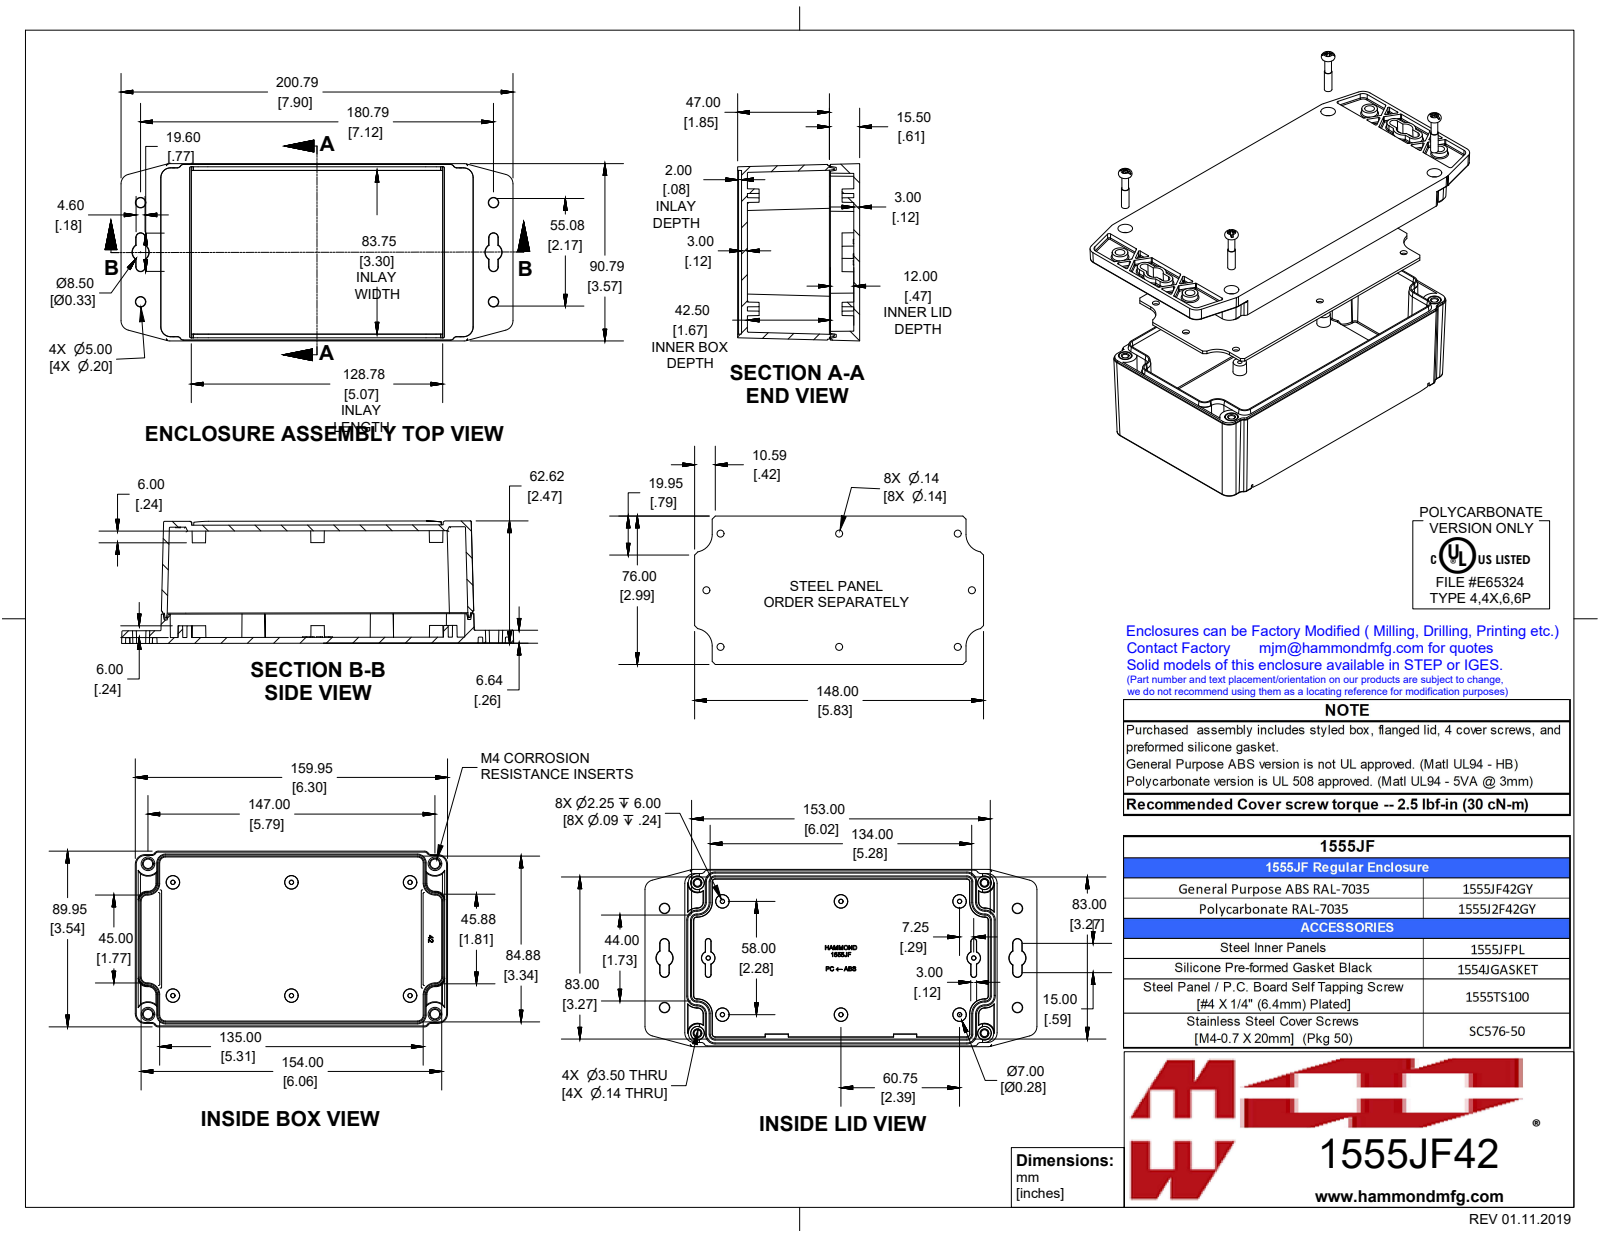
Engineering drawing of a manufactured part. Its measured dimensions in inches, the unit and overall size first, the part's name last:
Units: inches
Overall size (bounding box): 7.905 × 3.574 × 2.461
Round holes (diameter × count): ⌀0.128 ×4, ⌀0.138 ×4, ⌀0.276 ×4, ⌀0.374 ×1
Round bosses / shafts (diameter × count): ⌀0.25 ×4, ⌀0.218 ×4, ⌀0.21 ×4, ⌀0.153 ×4, ⌀0.135 ×4
Partial cylindrical surfaces — rounded edges, fillets, slot ends (radius × count): R0.02 ×104, R0.197 ×16, R0.089 ×4, R0.187 ×3, R1.988 ×1, R2.016 ×1, R2.126 ×1, R2.13 ×1
Main face-to-face distances: 0.118, 2.264, 2.382, 2.146, 0.059, 0.079, 0.472, 1.791, 1.673, 0.591
Hole centre spacings: 3.031, 5.787, 6.533
Volume: 13.23 in³ · Surface area: 226.9 in²
Bodies: 10 solids, 1338 faces (633 planar, 227 cylindrical, 478 other)
Part name (STEP PRODUCT): 1555JF42GY
STEP written by: SolidWorks 2019 (CONFIG_CONTROL_DESIGN)
